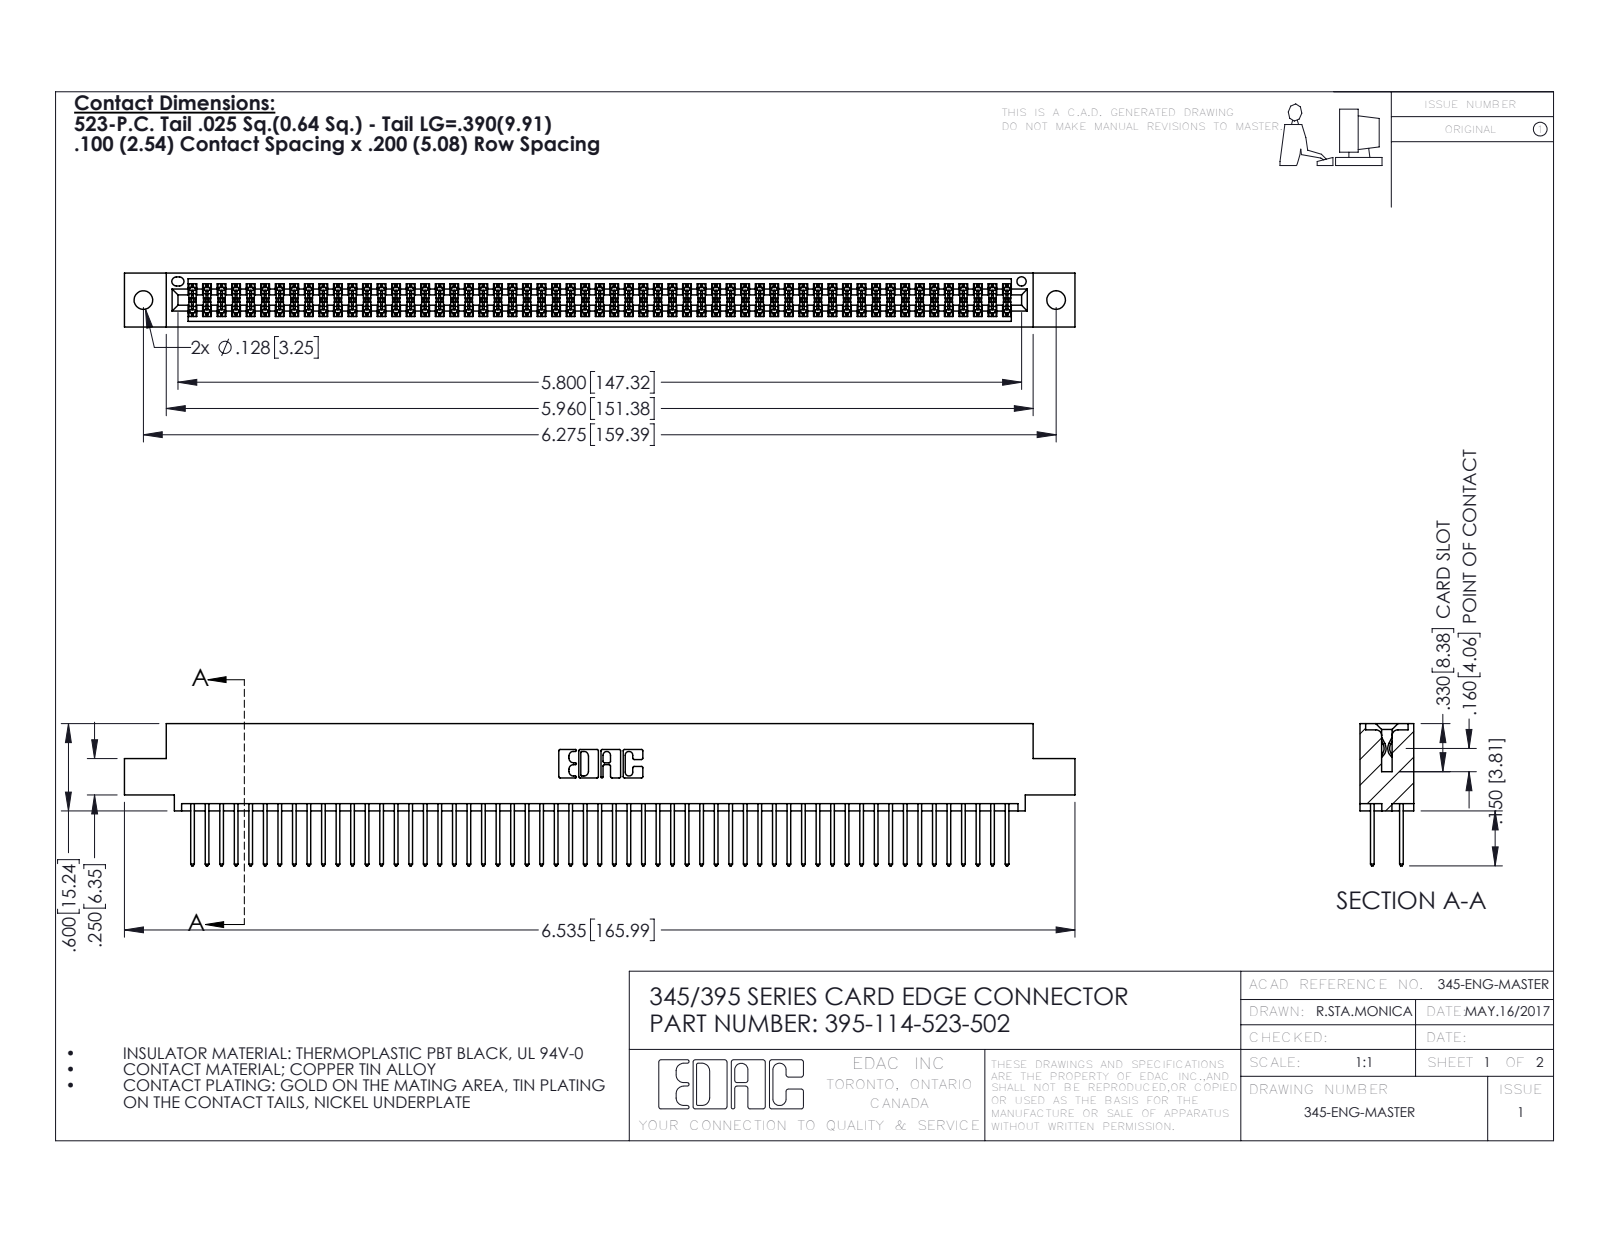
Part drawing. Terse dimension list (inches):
name: 345 Part_0.110 Offset - 0.128 Dia; 345-292-001_345-293-123; 395-114-523-502
written by: SolidWorks 2016 (CONFIG_CONTROL_DESIGN)
unit: in
bodies: 115 solids, 5830 faces (3846 planar, 1984 cylindrical, 0 other)
size: 6.535 × 0.977 × 0.37
volume: 1 in³; area: 39.34 in²
holes: 2× ⌀0.128, 1× ⌀0.064
rounds: 171× R0.006, 114× R0.01, 22× R0.01, 6× R0.007, 6× R0.031, 3× R0.026, 2× R0.014, 2× R0.019
face distances: 0.298, 0.072, 0.2, 0.098, 0.272, 0.025, 0.37, 0.225, 0.175, 0.149
hole spacings: 0.27, 6.039, 6.275
